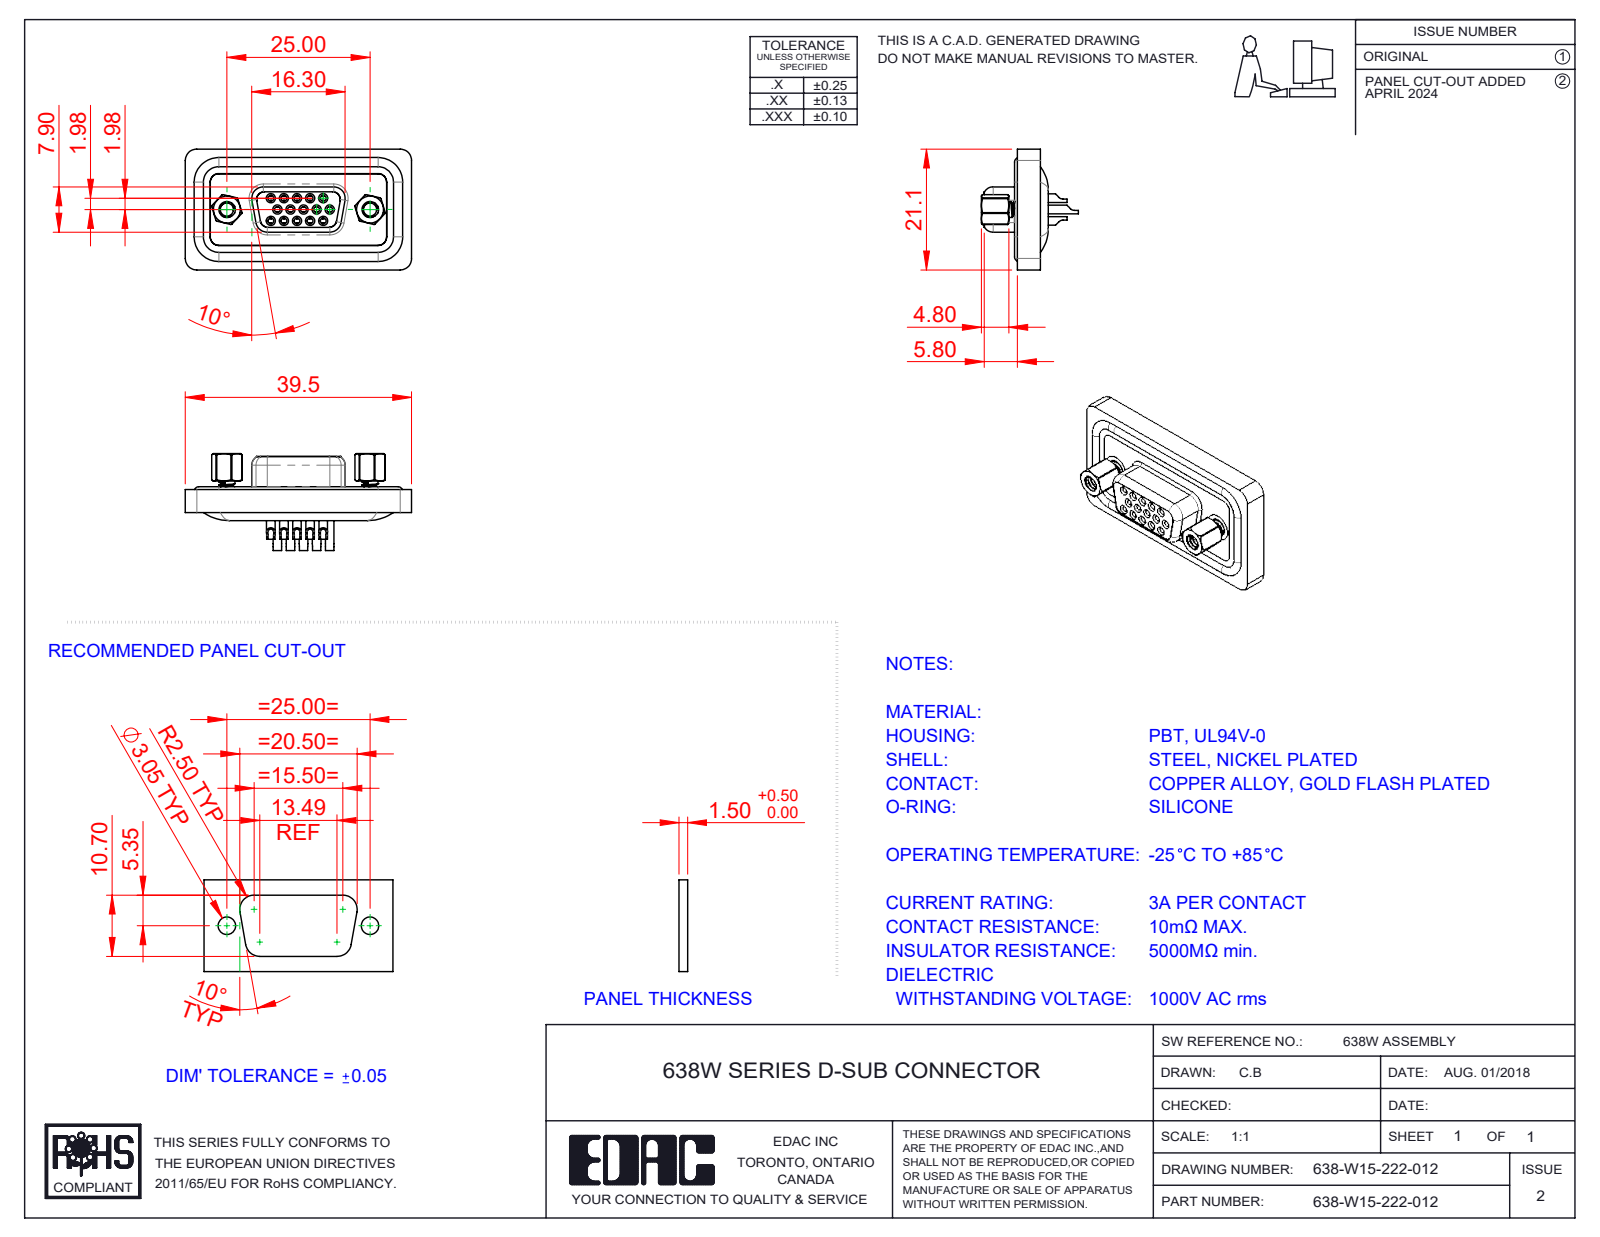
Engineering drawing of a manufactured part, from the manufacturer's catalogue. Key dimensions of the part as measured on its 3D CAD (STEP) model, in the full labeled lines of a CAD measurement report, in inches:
Part name (STEP PRODUCT): 638-W15-222-012; 638W Contact Row 2_22; 638W Waterproof Housing_15 Contacts; 638W 4-40 Threaded Rivet (+5 more)
STEP written by: SolidWorks 2023 (CONFIG_CONTROL_DESIGN)
Units: inches
Bodies: 23 solids, 1278 faces (356 planar, 565 cylindrical, 357 other)
Overall size (bounding box): 1.556 × 0.831 × 0.667
Volume: 0.264 in³ · Surface area: 12.69 in²
Round holes (diameter × count): ⌀0.039 ×16, ⌀0.043 ×15, ⌀0.059 ×15, ⌀0.067 ×15, ⌀0.071 ×15, ⌀0.079 ×15, ⌀0.089 ×2, ⌀0.09 ×2, ⌀0.157 ×2, ⌀0.189 ×2, ⌀0.197 ×2
Round bosses / shafts (diameter × count): ⌀0.063 ×19, ⌀0.087 ×15, ⌀0.059 ×6, ⌀0.193 ×2, ⌀0.11 ×2, ⌀0.197 ×1
Partial cylindrical surfaces — rounded edges, fillets, slot ends (radius × count): R0.059 ×14, R0.079 ×14, R0.053 ×8, R0.106 ×6, R0.02 ×4, R0.035 ×4, R0.063 ×4, R0.069 ×4
Main face-to-face distances: 0.016, 0.114, 0.063, 0.043, 0.098, 0.071, 0.02, 0.028, 0.142, 0.157
Hole centre spacings: 0.09, 0.156, 0.09, 0.18, 0.238, 0.238, 0.156, 0.324
